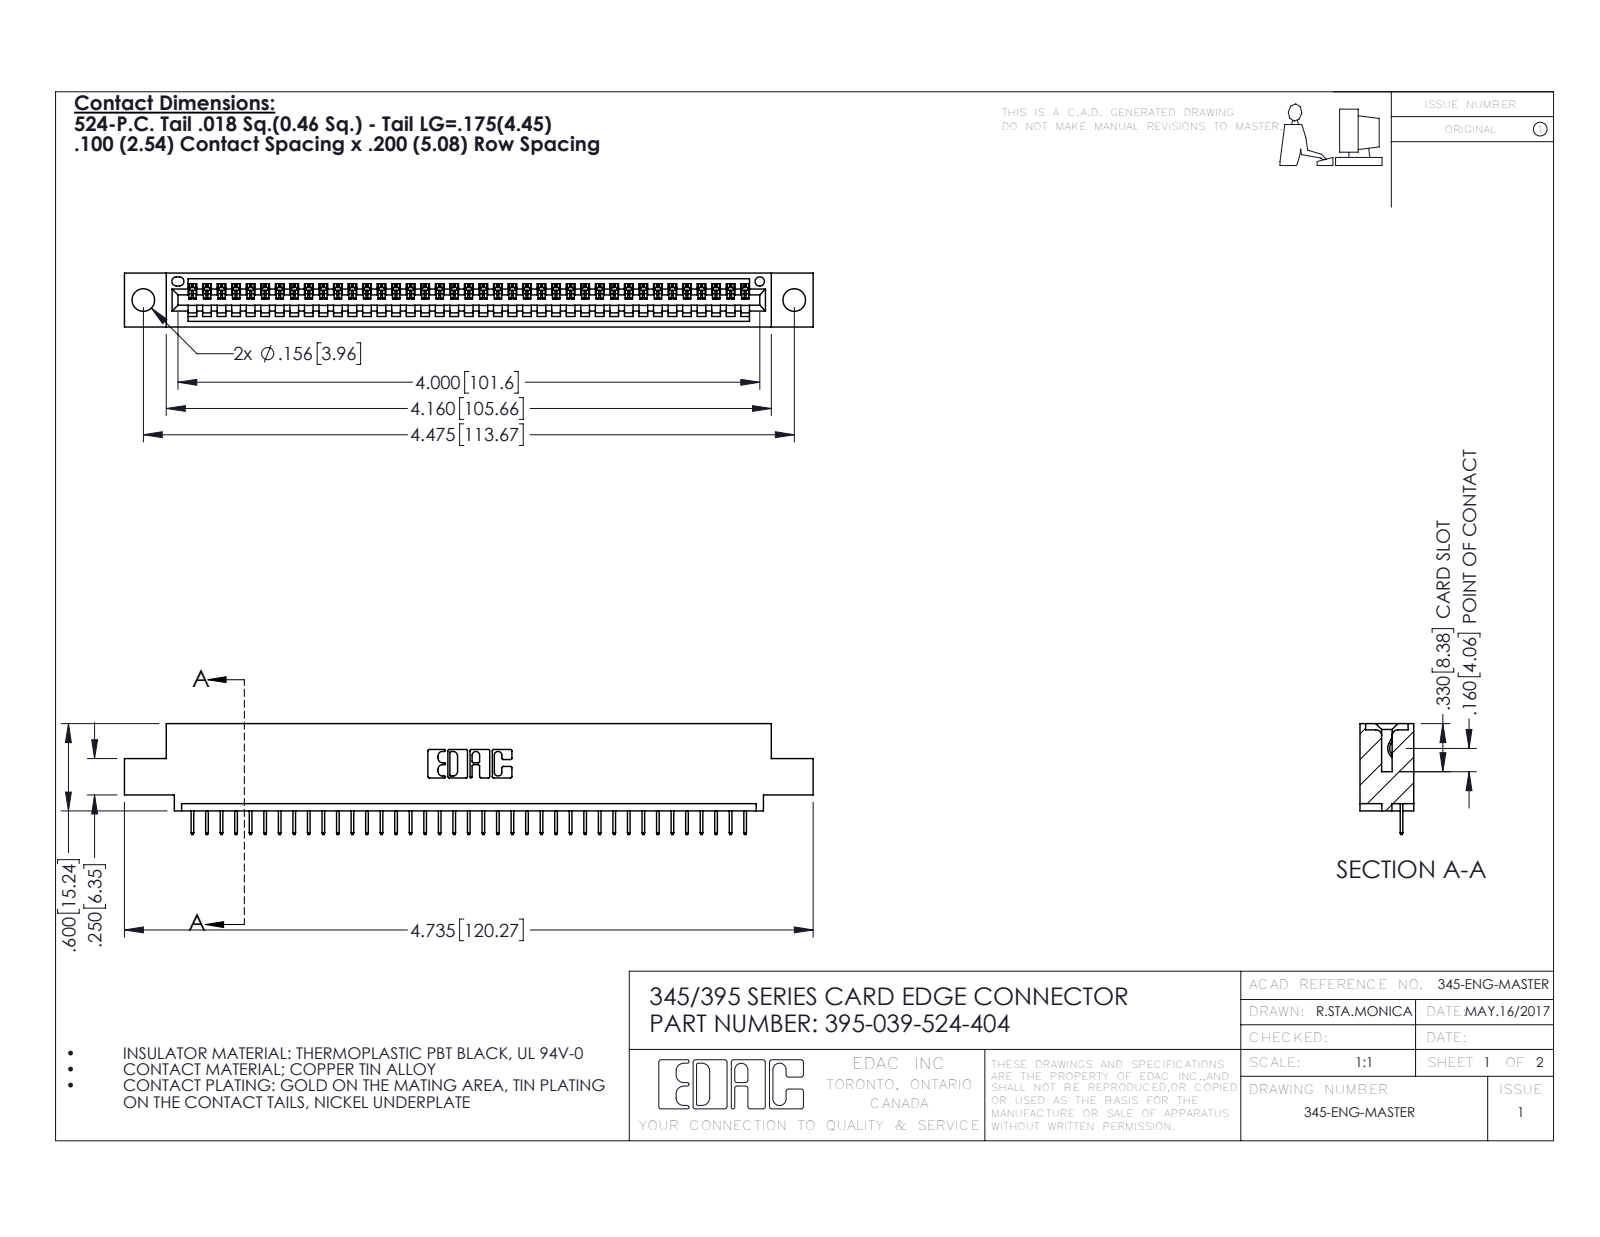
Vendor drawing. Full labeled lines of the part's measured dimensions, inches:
Part name (STEP PRODUCT): 395-039-524-404; 345-292-001_345-293-124; 345 Part_0.110 Offset - 0.156 Dia-TH
STEP written by: SolidWorks 2016 (CONFIG_CONTROL_DESIGN)
Units: inches
Bodies: 40 solids, 2548 faces (1878 planar, 670 cylindrical, 0 other)
Overall size (bounding box): 4.735 × 0.762 × 0.37
Volume: 0.676 in³ · Surface area: 21.83 in²
Round holes (diameter × count): ⌀0.156 ×2, ⌀0.064 ×1
Partial cylindrical surfaces — rounded edges, fillets, slot ends (radius × count): R0.006 ×78, R0.01 ×22, R0.007 ×6, R0.031 ×6, R0.026 ×3, R0.031 ×2, R0.04 ×2, R0.014 ×1
Main face-to-face distances: 0.072, 0.298, 0.37, 0.2, 0.098, 0.272, 0.025, 0.225, 0.072, 0.149
Hole centre spacings: 0.27, 4.239, 4.475
